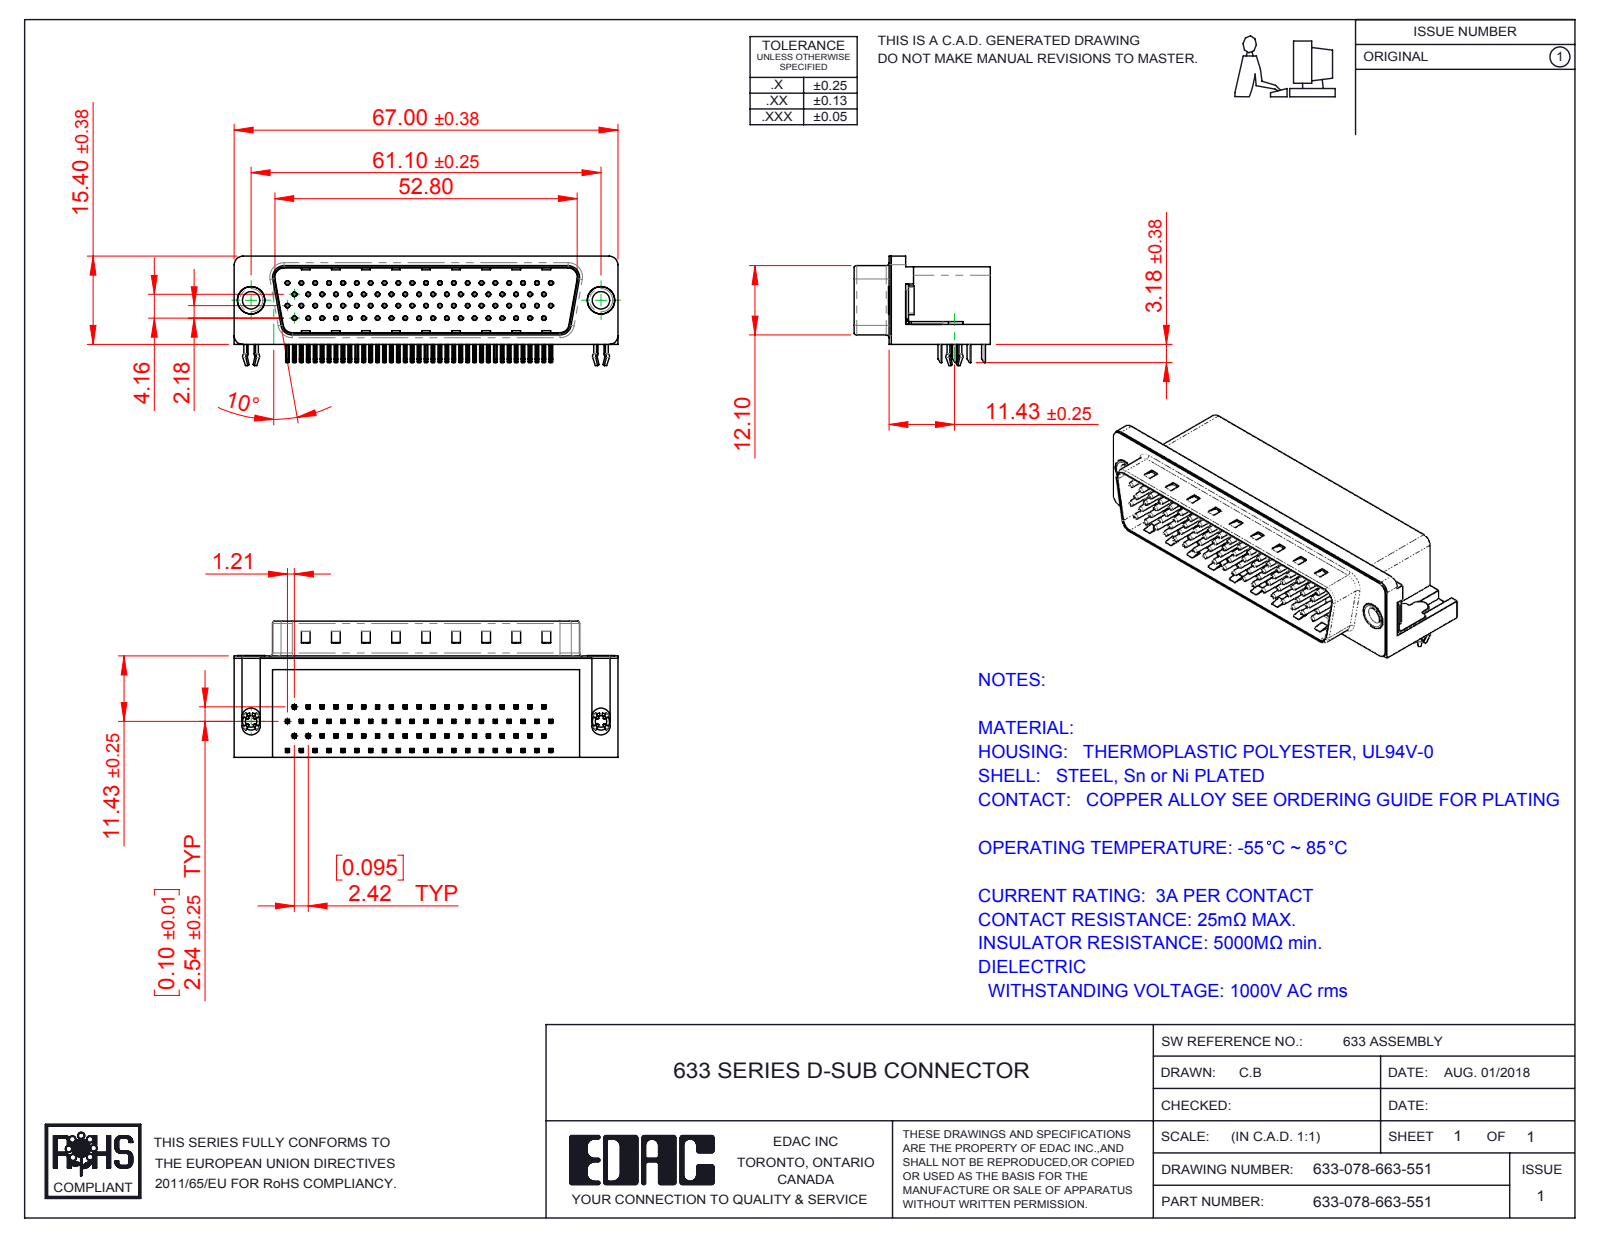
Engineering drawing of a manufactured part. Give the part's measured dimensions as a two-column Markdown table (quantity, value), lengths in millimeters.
| quantity | value |
| --- | --- |
| part name | 633 Contact Top_78 Contact; 633-078-663-551; 633 Thru Hole Rivet; 633 4 Prong Board Lock_78 Contact (+5 more) |
| STEP written by | SolidWorks 2016 (CONFIG_CONTROL_DESIGN) |
| units | millimeters |
| bodies | 84 solids, 6356 faces (4023 planar, 1766 cylindrical, 567 other) |
| overall size | 67 × 23.8 × 19.1 |
| volume | 14 611 mm³ |
| surface area | 16 410 mm² |
| round holes (diameter × count) | 0.35 × 78, 0.8 × 78, 2 × 2, 3.05 × 2, 4 × 2, 4.8 × 2, 5 × 2 |
| round bosses / shafts (diameter × count) | 0.75 × 78, 4.9 × 2, 4.75 × 2, 3.85 × 2, 3 × 2 |
| partial cylindrical surfaces (radius × count) | 0.25 × 324, 0.12 × 156, 1 × 16, 0.5 × 9, 1.6 × 8, 1.5 × 6, 0.45 × 4, 0.9 × 4 |
| main face-to-face distances | 0.4, 13.2, 17.3, 11.7, 13.35, 2.05, 13.75, 1.65, 1.85, 11.9 |
| hole center spacings | 2.42, 4.84, 7.26, 9.68, 6.26, 7.13, 12.1, 8.62 |
